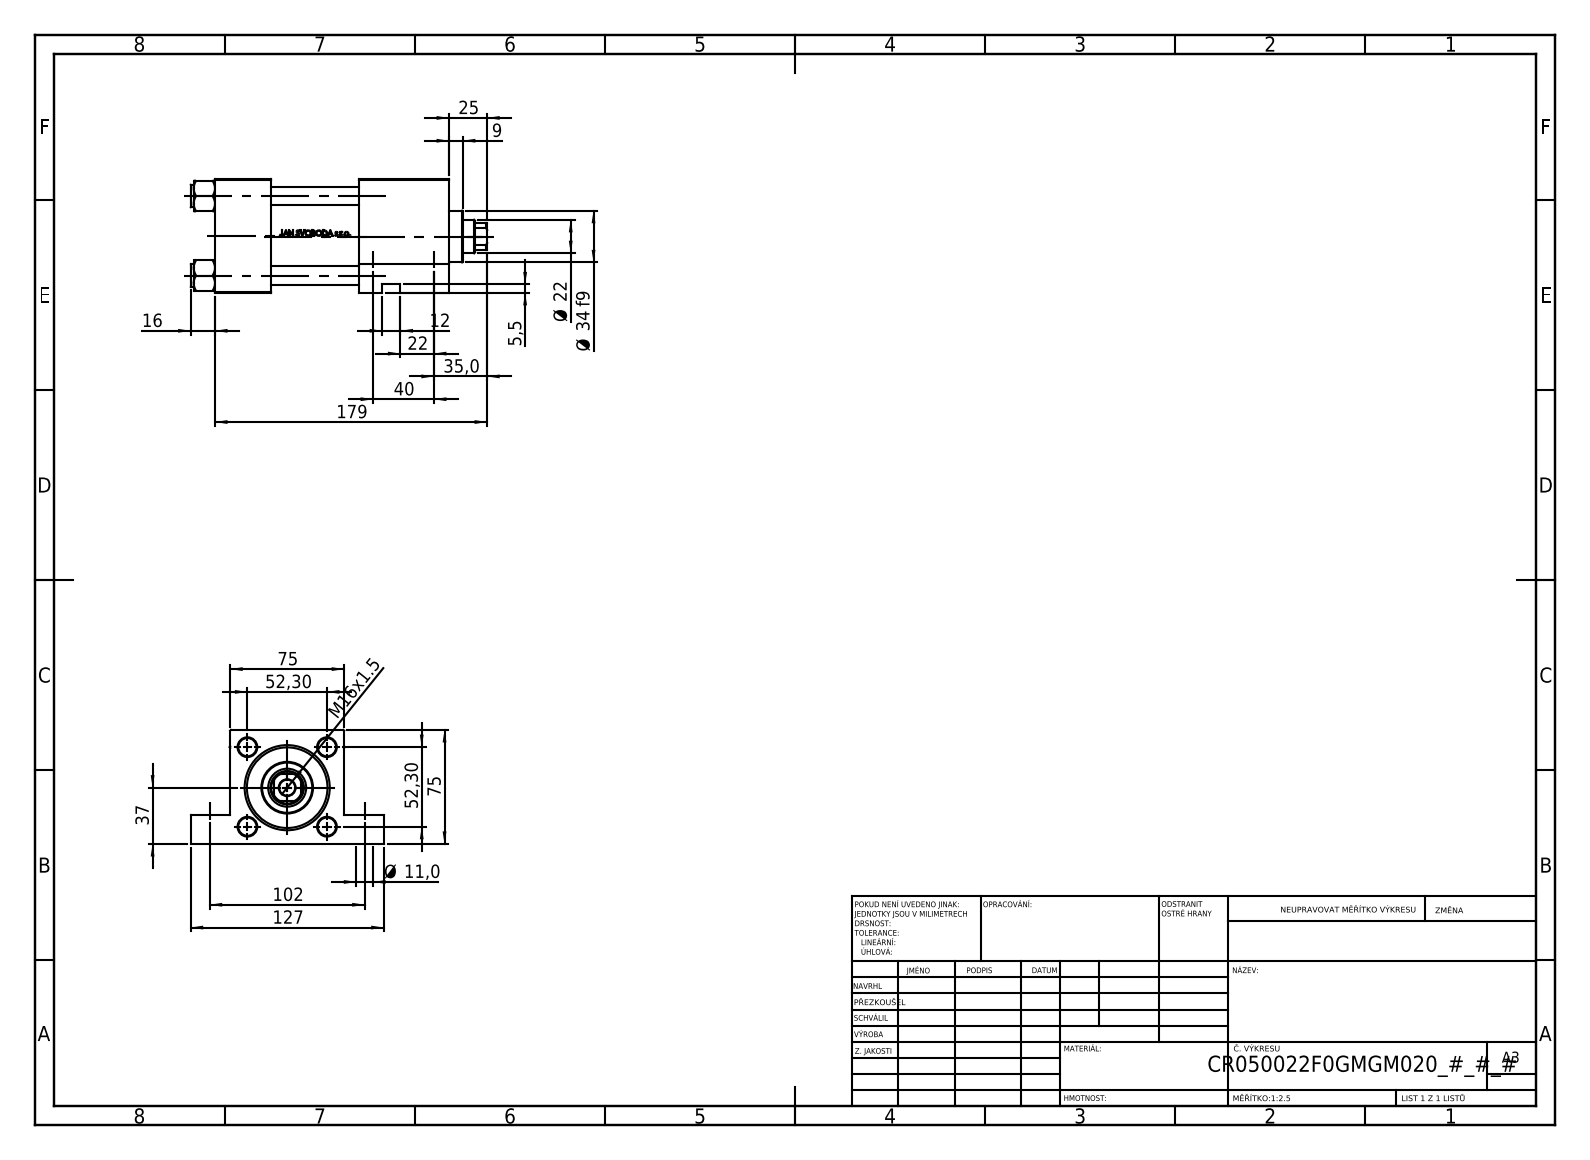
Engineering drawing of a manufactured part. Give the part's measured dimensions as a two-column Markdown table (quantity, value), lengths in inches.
| quantity | value |
| --- | --- |
| part name | V215CR_VCP_F; V215_VC_A; V215CR_F_Body; V215CR_F_TYCINKA (+1 more) |
| STEP written by | SolidWorks 2019 (CONFIG_CONTROL_DESIGN) |
| units | inches |
| bodies | 11 solids, 1103 faces (437 planar, 126 cylindrical, 540 other) |
| overall size | 7.677 × 5 × 2.953 |
| volume | 43.13 in³ |
| surface area | 242.3 in² |
| round holes (diameter × count) | 0.472 × 4, 0.276 × 2, 0.433 × 2, 0.433 × 2, 1.181 × 2, 0.413 × 1, 0.669 × 1, 0.825 × 1, 0.866 × 1, 0.984 × 1, 1.614 × 1, 1.969 × 1 |
| round bosses / shafts (diameter × count) | 0.591 × 4, 2.205 × 1, 1.339 × 1 |
| partial cylindrical surfaces (radius × count) | 0.413 × 1 |
| main face-to-face distances | 2.953, 1.457, 4.606, 6.063, 3.74, 2.283, 2.323, 4.933, 3.476, 1.193 |
| hole center spacings | 2.059, 1.442, 1.47, 1.575, 2.912, 4.016, 4.313, 3.681 |
